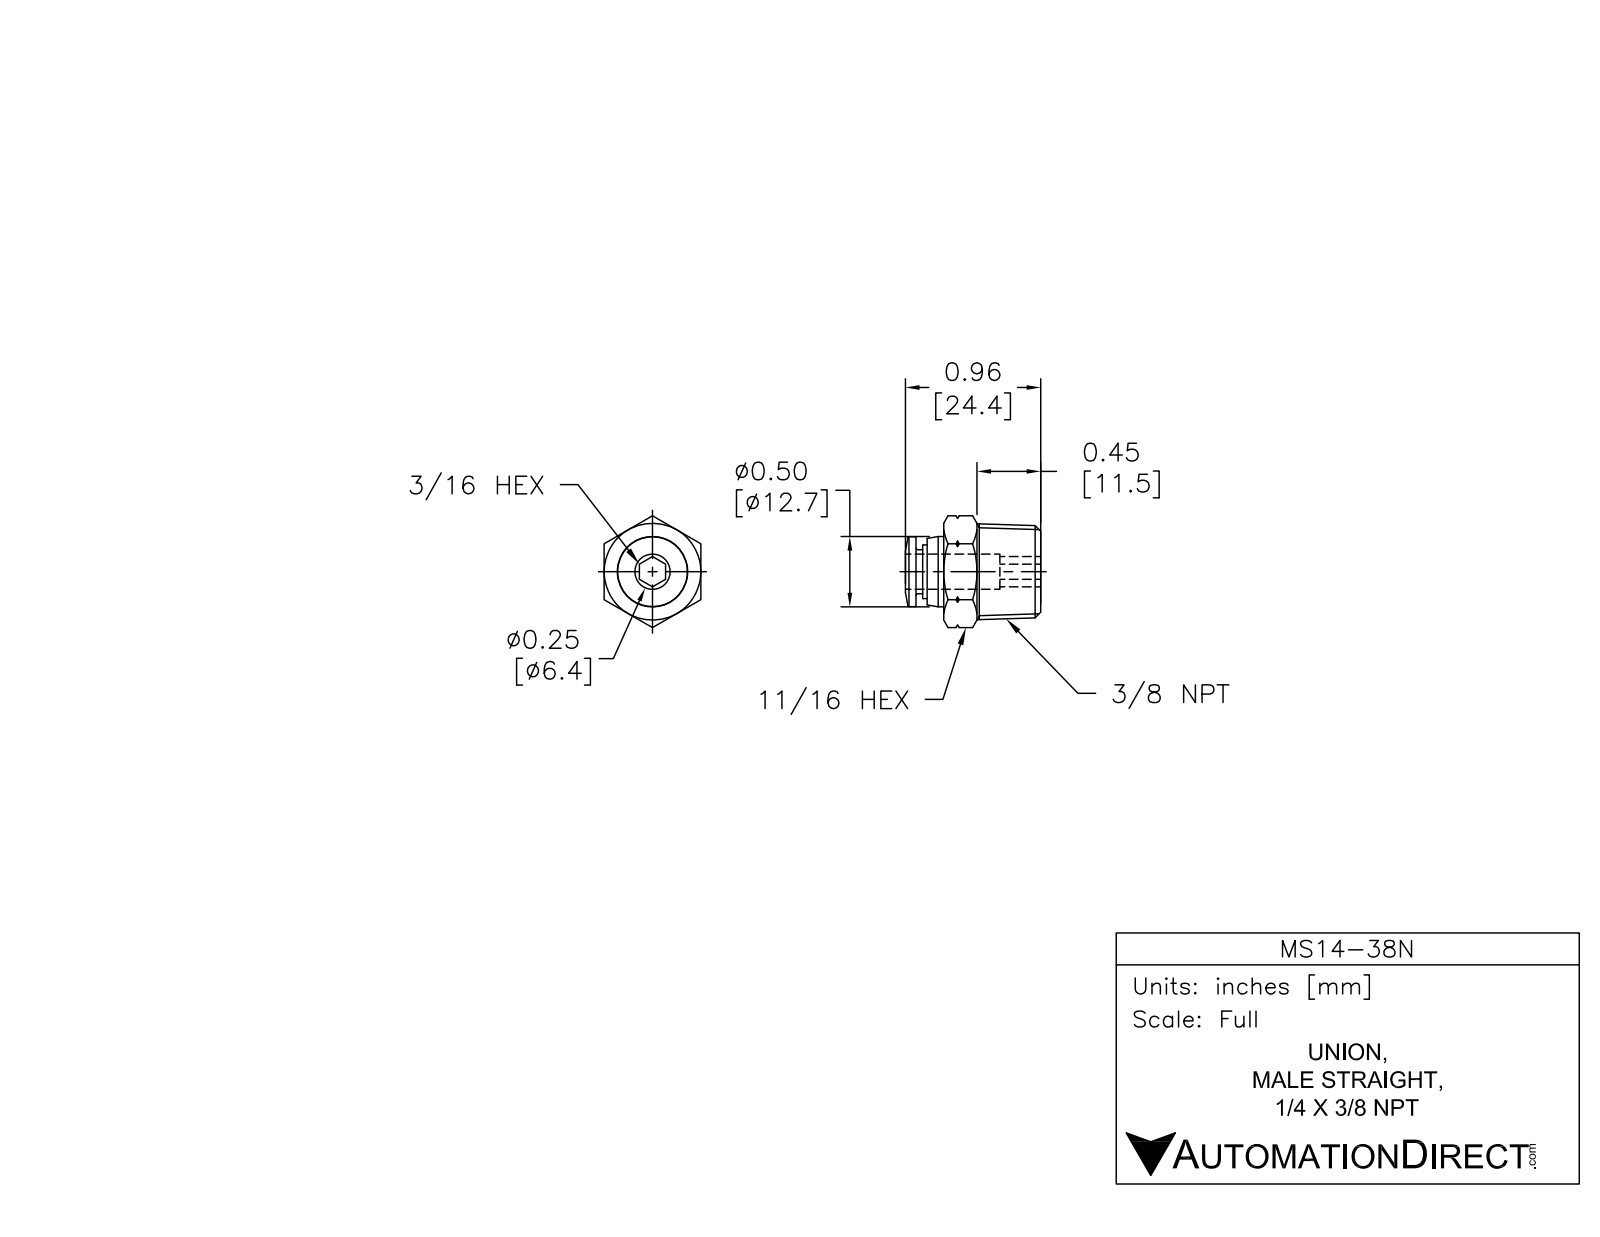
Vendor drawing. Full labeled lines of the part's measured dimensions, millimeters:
Part name (STEP PRODUCT): PC1-4--N03
STEP written by: Autodesk Inventor 2008 (AUTOMOTIVE_DESIGN)
Units: millimetres
Bodies: 1 solid, 51 faces (13 planar, 6 cylindrical, 32 other)
Overall size (bounding box): 24.4 × 20.16 × 17.46
Volume: 4 134 mm³ · Surface area: 2 214 mm²
Round holes (diameter × count): ⌀4.8 ×1, ⌀6.55 ×1
Round bosses / shafts (diameter × count): ⌀12.7 ×1, ⌀12.6 ×1, ⌀9.7 ×1, ⌀7.95 ×1
Main face-to-face distances: 17.46, 17.5, 22.5, 5, 20.5, 3, 2, 21.3, 3.8, 0.8
